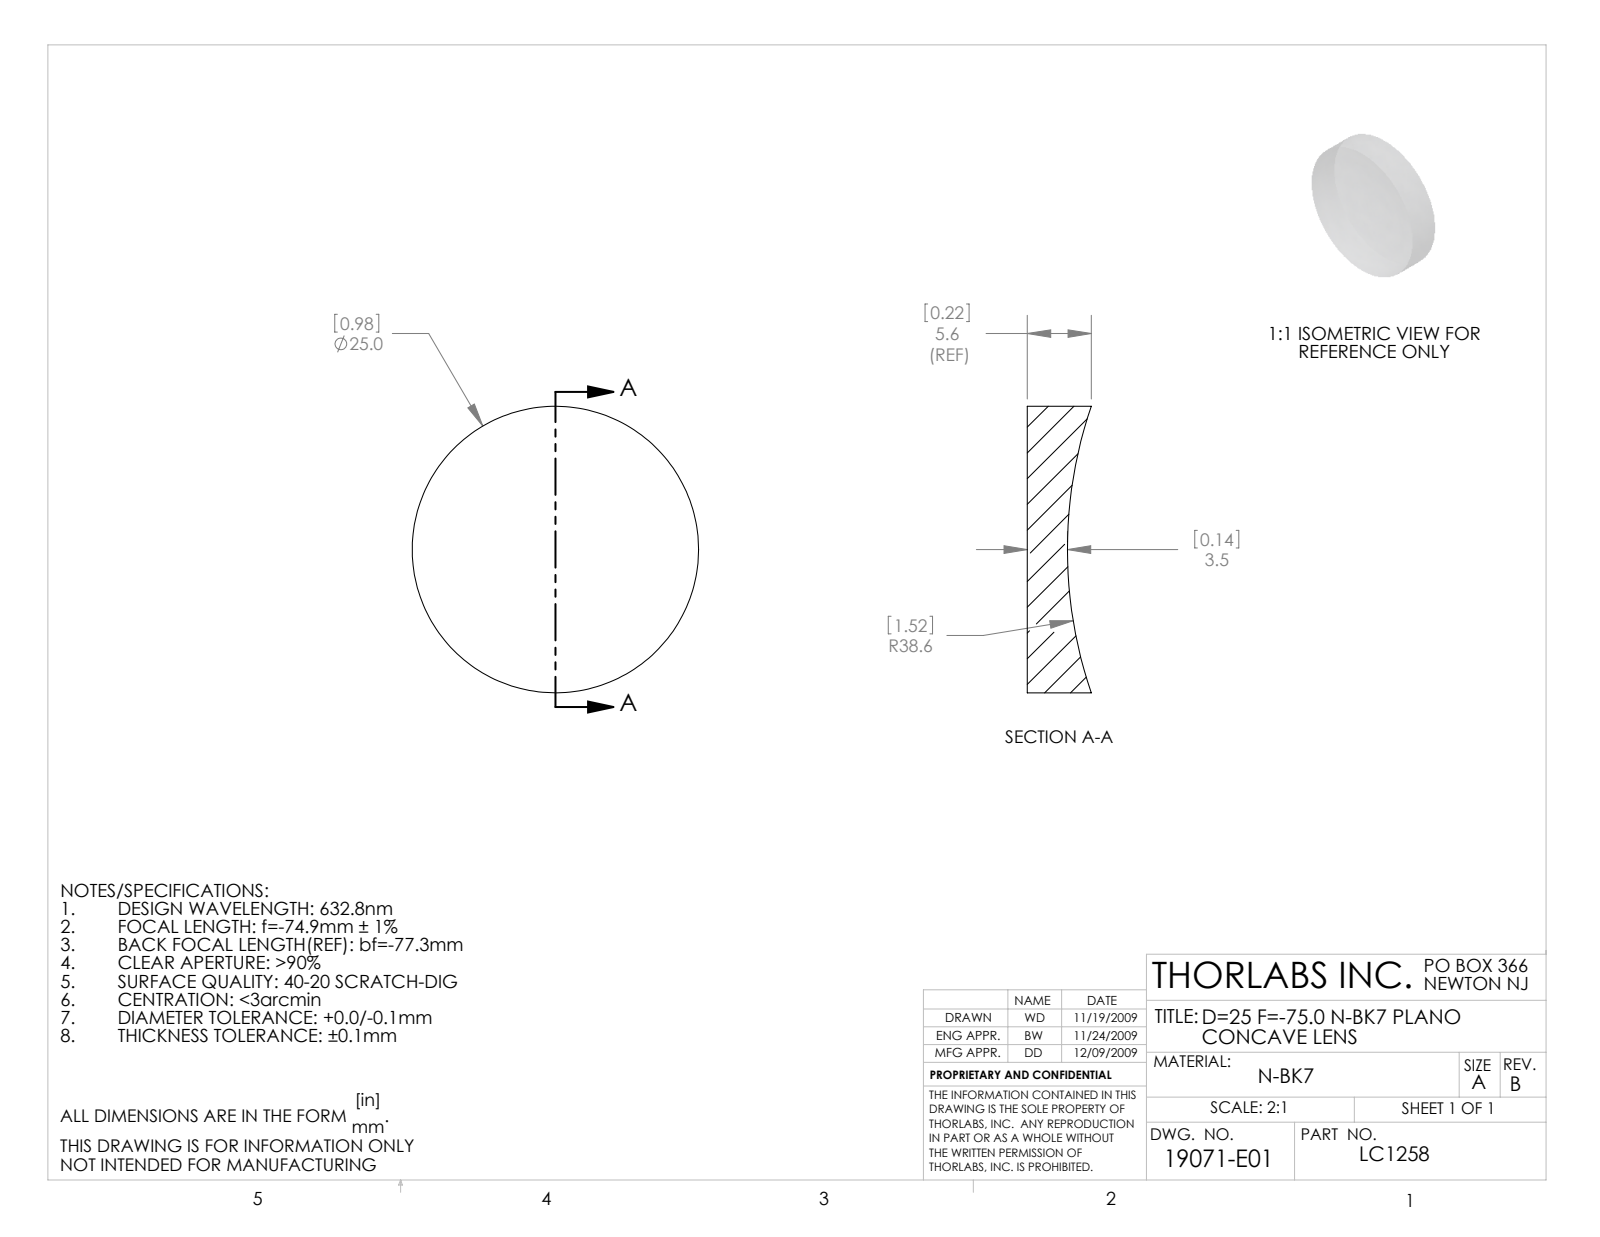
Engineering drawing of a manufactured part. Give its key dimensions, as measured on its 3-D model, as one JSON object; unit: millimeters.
{"part_name": "19071-E0W", "step_written_by": "SolidWorks 2009 (AUTOMOTIVE_DESIGN)", "units": "millimeters", "bodies": {"solids": 1, "faces": 5, "planar": 1, "cylindrical": 2, "other": 2}, "overall_size": [25, 25, 5.58], "volume_mm3": 2224, "surface_area_mm2": 1434, "round_bosses_or_shafts": [[25, 1]]}
